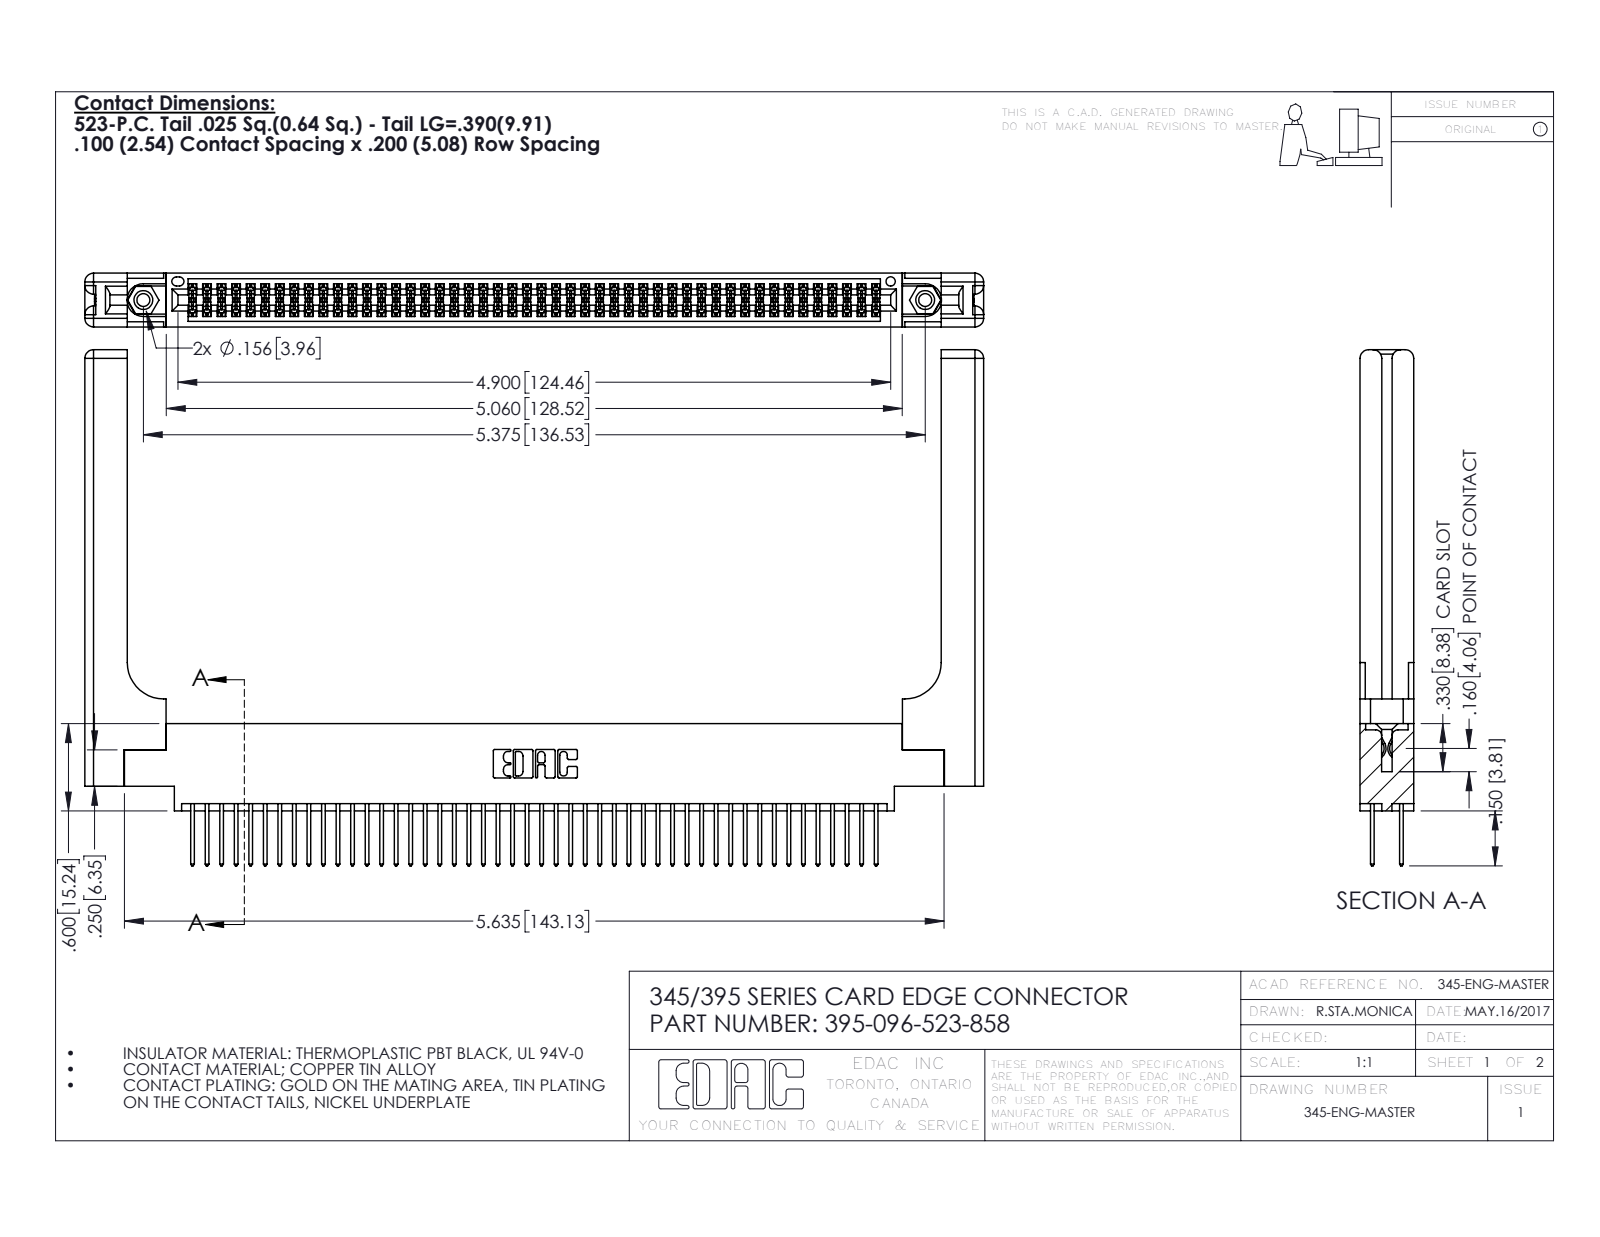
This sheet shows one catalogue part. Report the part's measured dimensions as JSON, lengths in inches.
{"part_name": "345-250-001_345-250-001-102; 345-292-001_345-293-123; 345-220-058_345-220-058; 395-096-523-858 (+1 more)", "step_written_by": "SolidWorks 2016 (CONFIG_CONTROL_DESIGN)", "units": "inches", "bodies": {"solids": 101, "faces": 5186, "planar": 3400, "cylindrical": 1726, "other": 60}, "overall_size": [6.179, 3.547, 0.37], "volume_in3": 1.456, "surface_area_in2": 44.86, "round_holes": [[0.089, 2], [0.125, 2], [0.156, 2], [0.064, 1]], "round_bosses_or_shafts": [[0.155, 2]], "partial_cylinders_radius": [[0.006, 144], [0.01, 96], [0.01, 22], [0.06, 16], [0.007, 6], [0.031, 6], [0.026, 3], [0.014, 2]], "face_to_face_distances": [0.072, 0.298, 0.37, 0.098, 0.272, 0.025, 0.2, 0.225, 0.175, 0.148], "hole_center_spacings": [0.27, 5.139, 5.375]}
